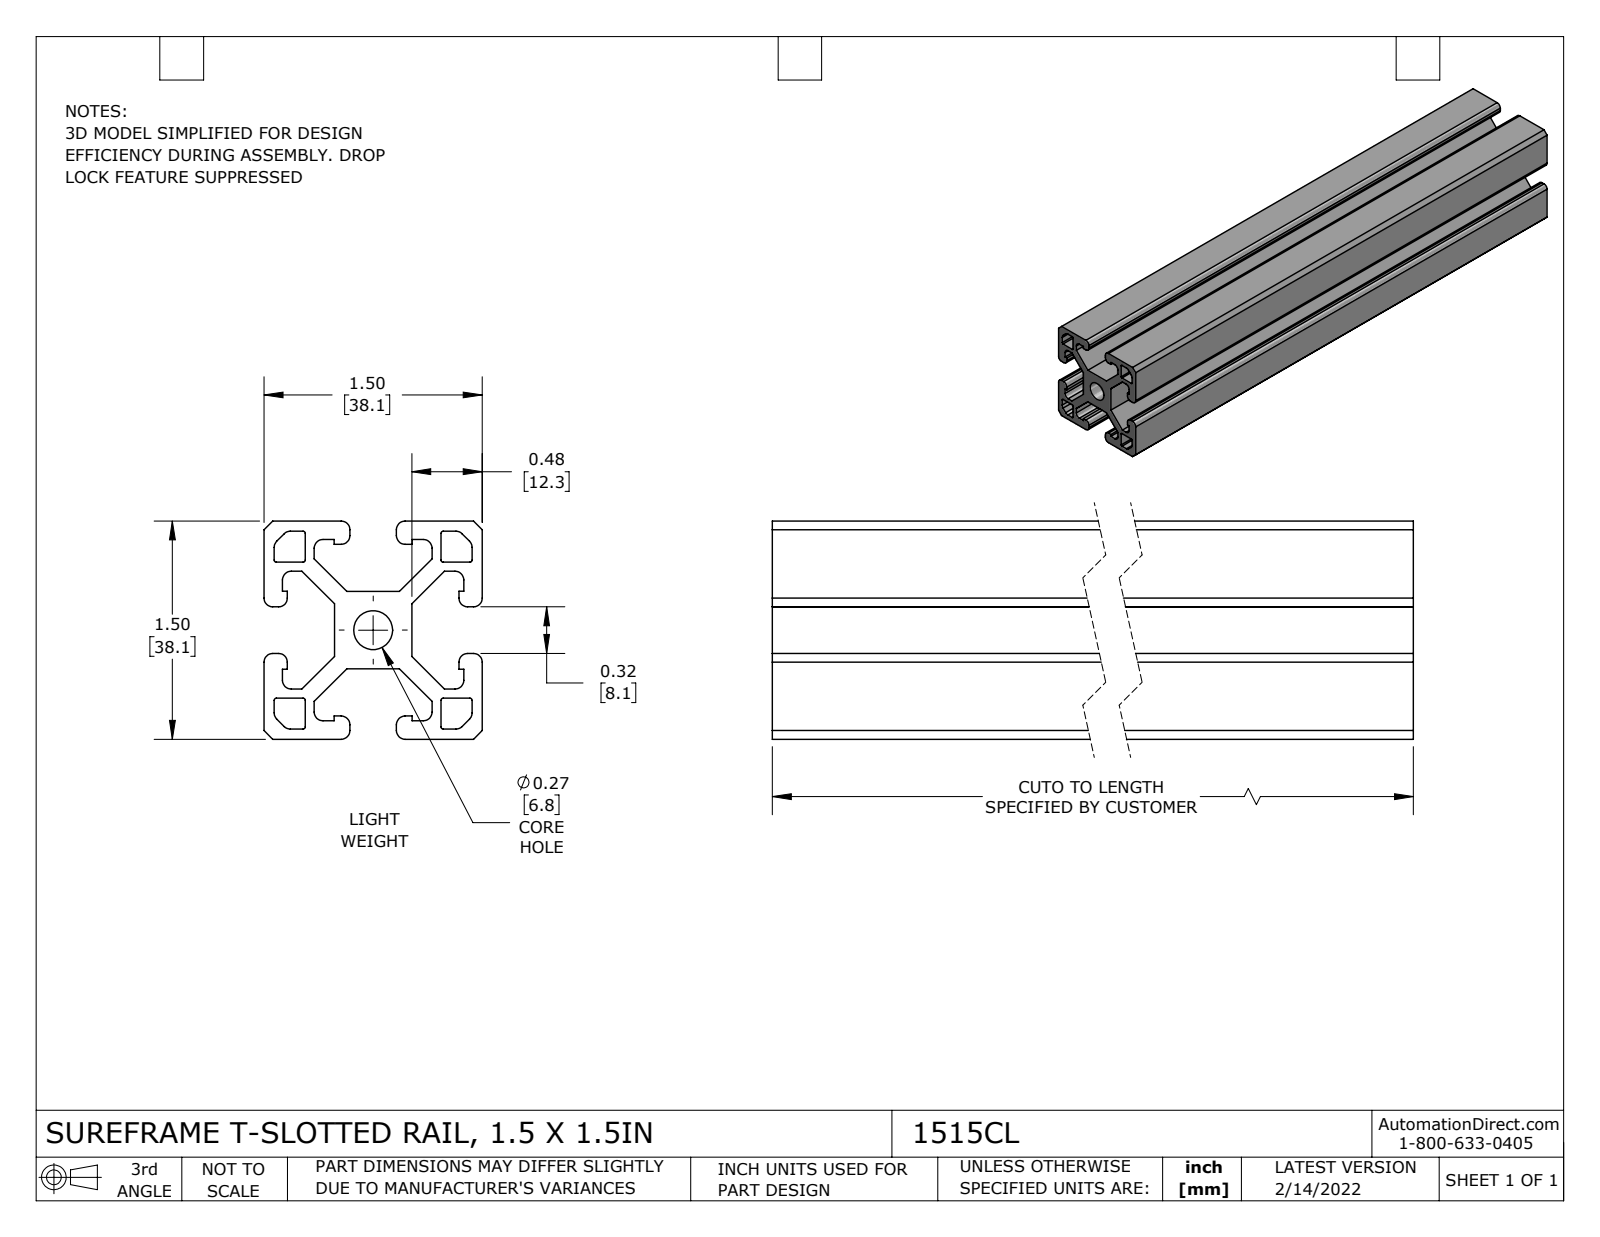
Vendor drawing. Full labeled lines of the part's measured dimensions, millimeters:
Part name (STEP PRODUCT): 1515CL
STEP written by: SolidWorks 2021 (CONFIG_CONTROL_DESIGN)
Units: millimetres
Bodies: 1 solid, 132 faces (86 planar, 46 cylindrical, 0 other)
Overall size (bounding box): 203.2 × 38.1 × 38.1
Volume: 121 200 mm³ · Surface area: 86 130 mm²
Round holes (diameter × count): ⌀6.8 ×1
Partial cylindrical surfaces — rounded edges, fillets, slot ends (radius × count): R1.5 ×32, R0.4 ×12
Main face-to-face distances: 38.1, 7.2, 30.9, 12.3, 25.8, 5.1, 18.6, 3, 23.7, 13.5
